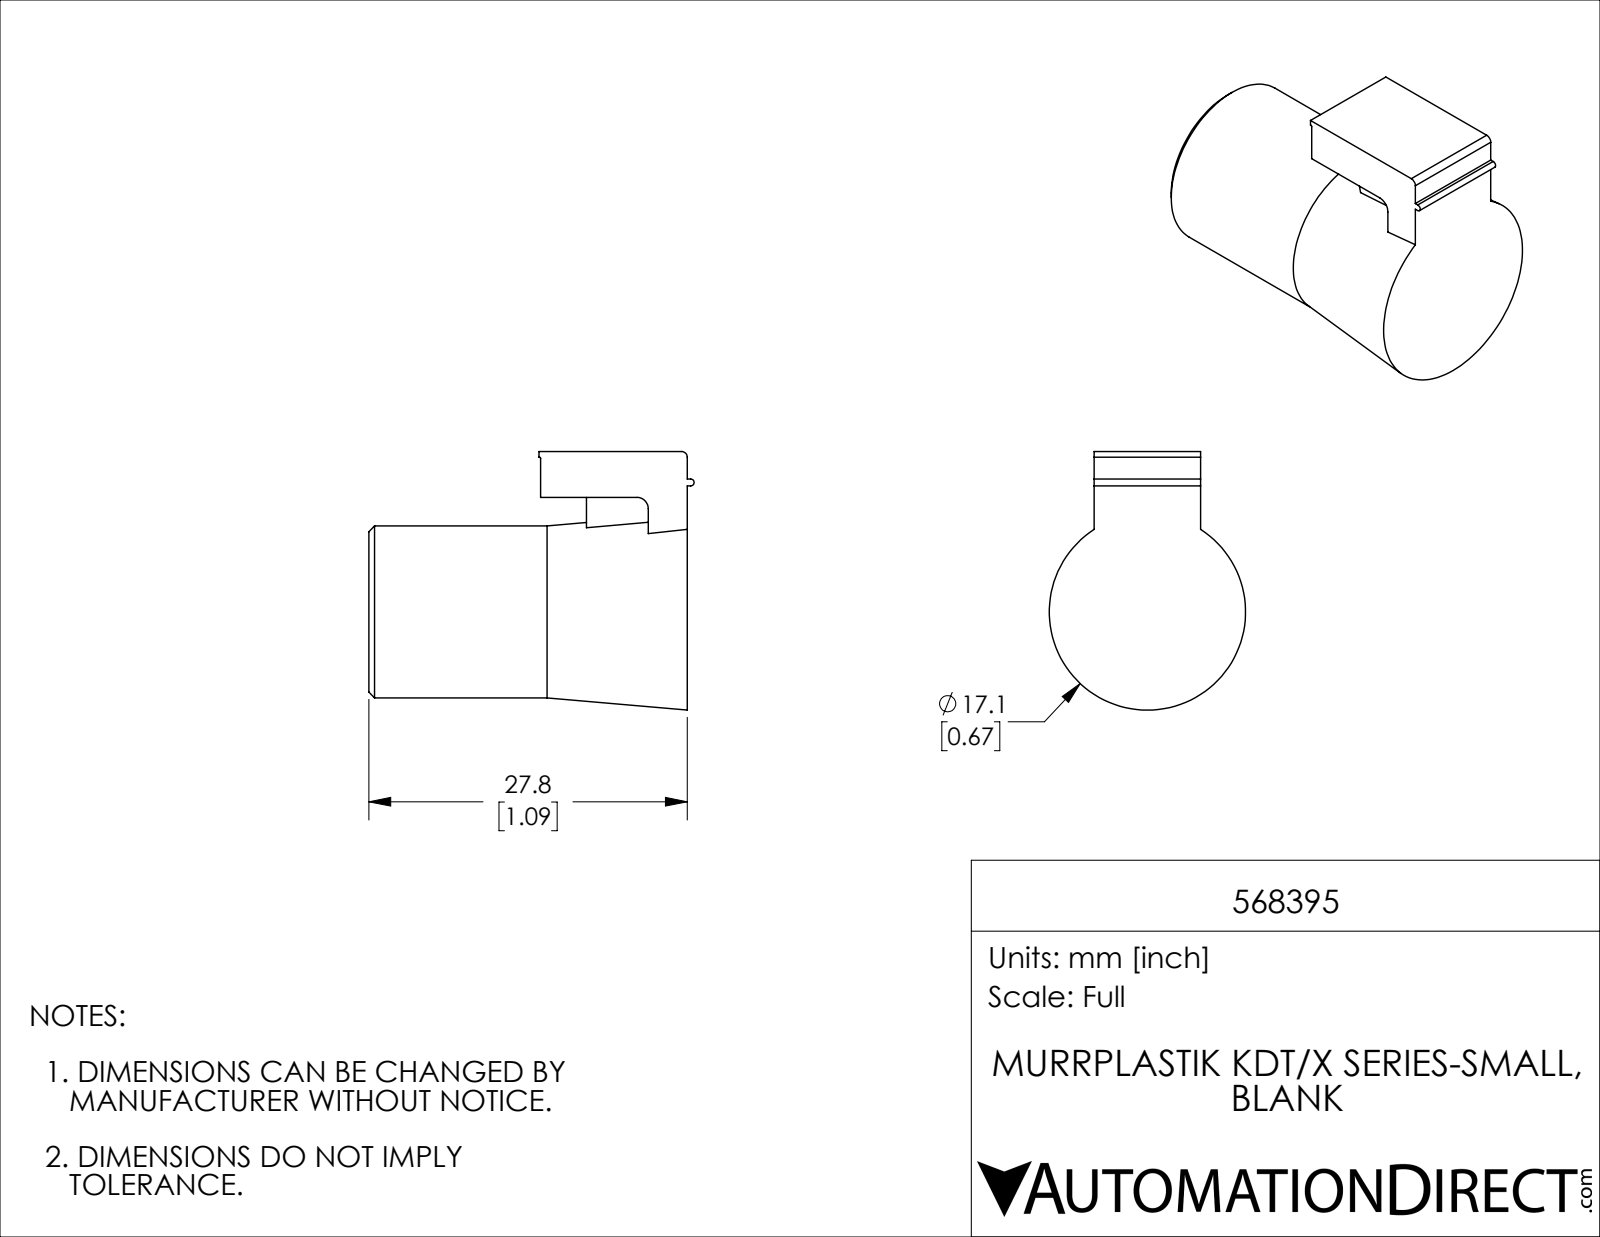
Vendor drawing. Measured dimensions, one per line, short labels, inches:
name: 568395
written by: SolidWorks 2019 (CONFIG_CONTROL_DESIGN)
unit: in
bodies: 1 solid, 45 faces (28 planar, 10 cylindrical, 7 other)
size: 1.118 × 0.889 × 0.675
volume: 0.303 in³; area: 4.064 in²
holes: 1× ⌀0.276
bosses: 1× ⌀0.591
rounds: 1× R0.004, 1× R0.012, 1× R0.02, 1× R0.039
face distances: 1.094, 0.157, 0.366, 0.504, 0.591, 0.346, 0.748, 0.134, 0.213, 0.37
